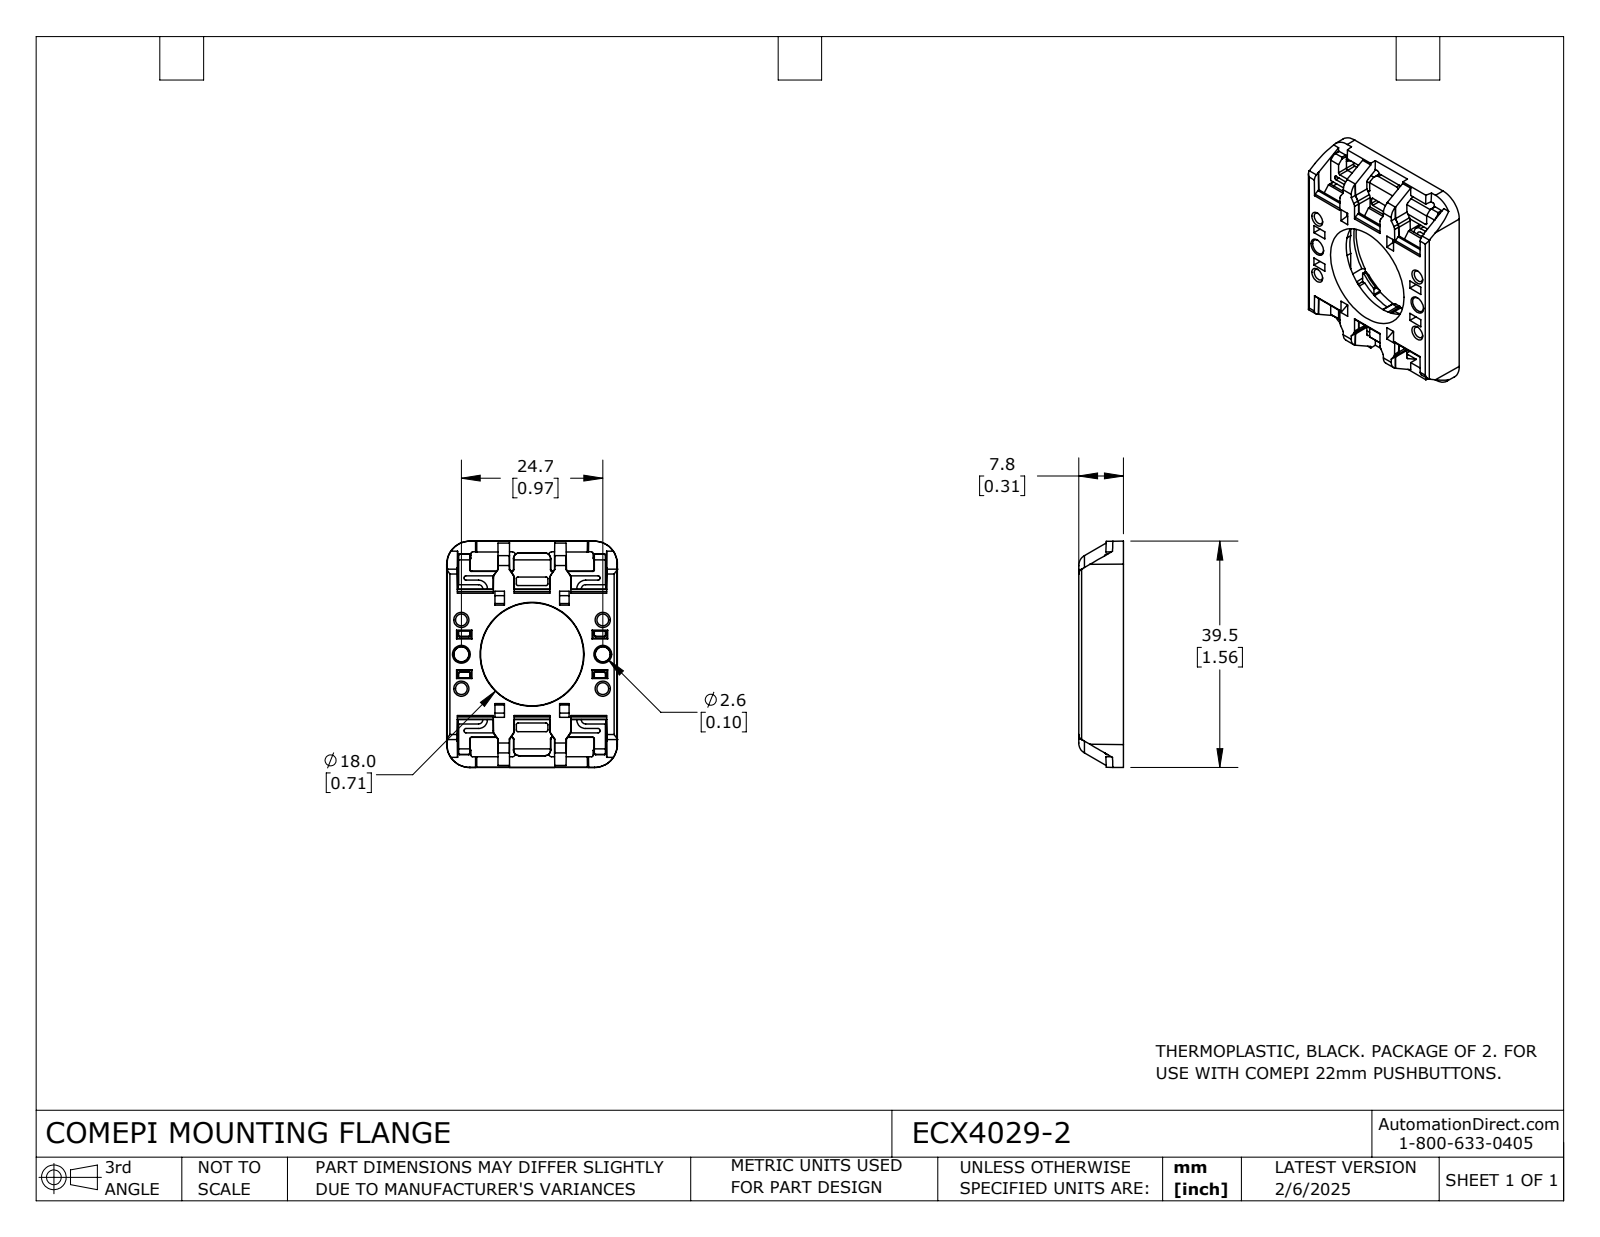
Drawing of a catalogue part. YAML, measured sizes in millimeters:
part_name: "ECX4029-2"
step_written_by: "SolidWorks 2024 (CONFIG_CONTROL_DESIGN)"
units: millimeters
bodies: {solids: 3, faces: 856, planar: 424, cylindrical: 332, other: 100}
overall_size: [39.5, 29.8, 7.8]
volume: 3720
surface_area: 5744
round_holes:
  - {diameter: 2.1, count: 4}
partial_cylinders:
  - {radius: 0.3, count: 72}
  - {radius: 0.2, count: 32}
  - {radius: 1, count: 22}
  - {radius: 0.5, count: 12}
  - {radius: 0.9, count: 8}
  - {radius: 4, count: 4}
  - {radius: 2, count: 2}
  - {radius: 9.7, count: 1}
face_to_face_distances: [3.8, 4, 7.8, 3.7, 22.8, 7.5, 5.7, 1.5, 25.7, 3.9]
hole_center_spacings: [12, 24.7, 27.5]
